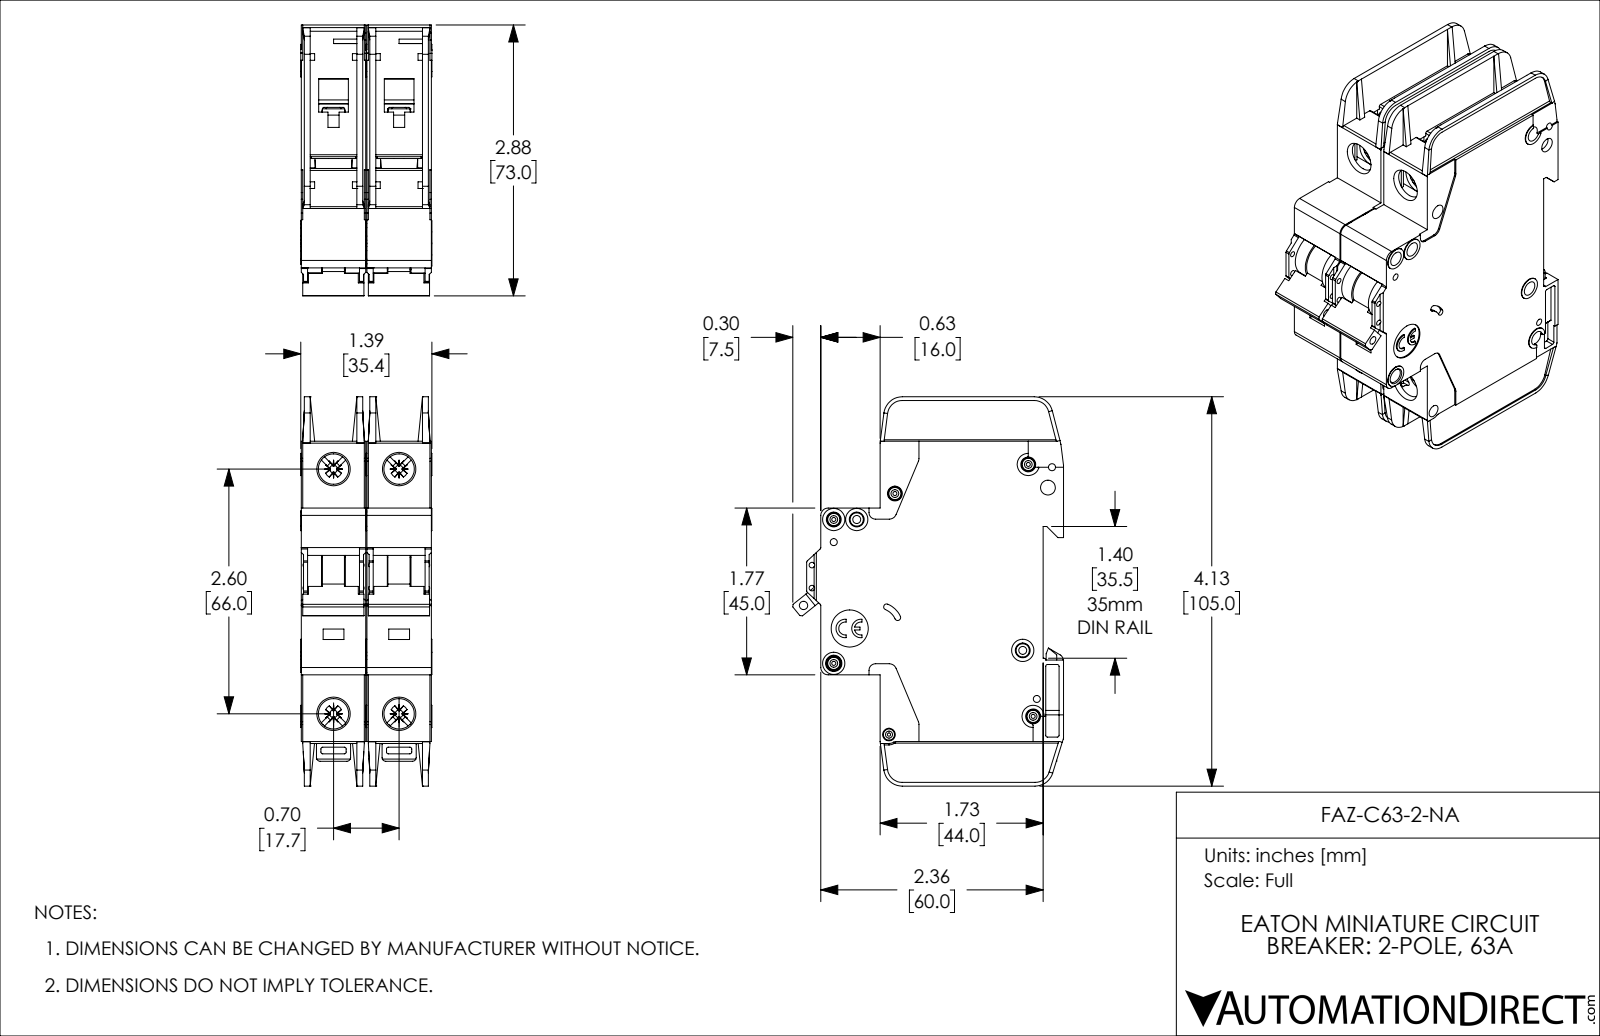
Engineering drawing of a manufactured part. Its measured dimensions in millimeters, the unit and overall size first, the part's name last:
Units: millimetres
Overall size (bounding box): 105 × 73.1 × 35.4
Round holes (diameter × count): ⌀4 ×8, ⌀1.1 ×5, ⌀1.9 ×4, ⌀8.2 ×4, ⌀1.5 ×2, ⌀2.2 ×2, ⌀0.9 ×1, ⌀2.3 ×1, ⌀2.5 ×1, ⌀3.4 ×1, ⌀10 ×1
Round bosses / shafts (diameter × count): ⌀3.3 ×5, ⌀6 ×4, ⌀3 ×3, ⌀2.5 ×2
Partial cylindrical surfaces — rounded edges, fillets, slot ends (radius × count): R0.5 ×57, R0.4 ×20, R1 ×14, R2 ×10, R1.1 ×8, R0.2 ×5, R5 ×5, R0.3 ×4
Main face-to-face distances: 17.7, 1.2, 17.4, 15, 2.4, 16.2, 13.8, 35.1, 18.9, 16.5
Hole centre spacings: 6.2, 13.6, 17.7, 22.1, 66, 68.3, 4.8, 5.1
Volume: 153 500 mm³ · Surface area: 52 910 mm²
Bodies: 2 solids, 2254 faces (1342 planar, 714 cylindrical, 198 other)
Part name (STEP PRODUCT): FAZ-C63-2-NA
STEP written by: SolidWorks 2019 (AUTOMOTIVE_DESIGN)
